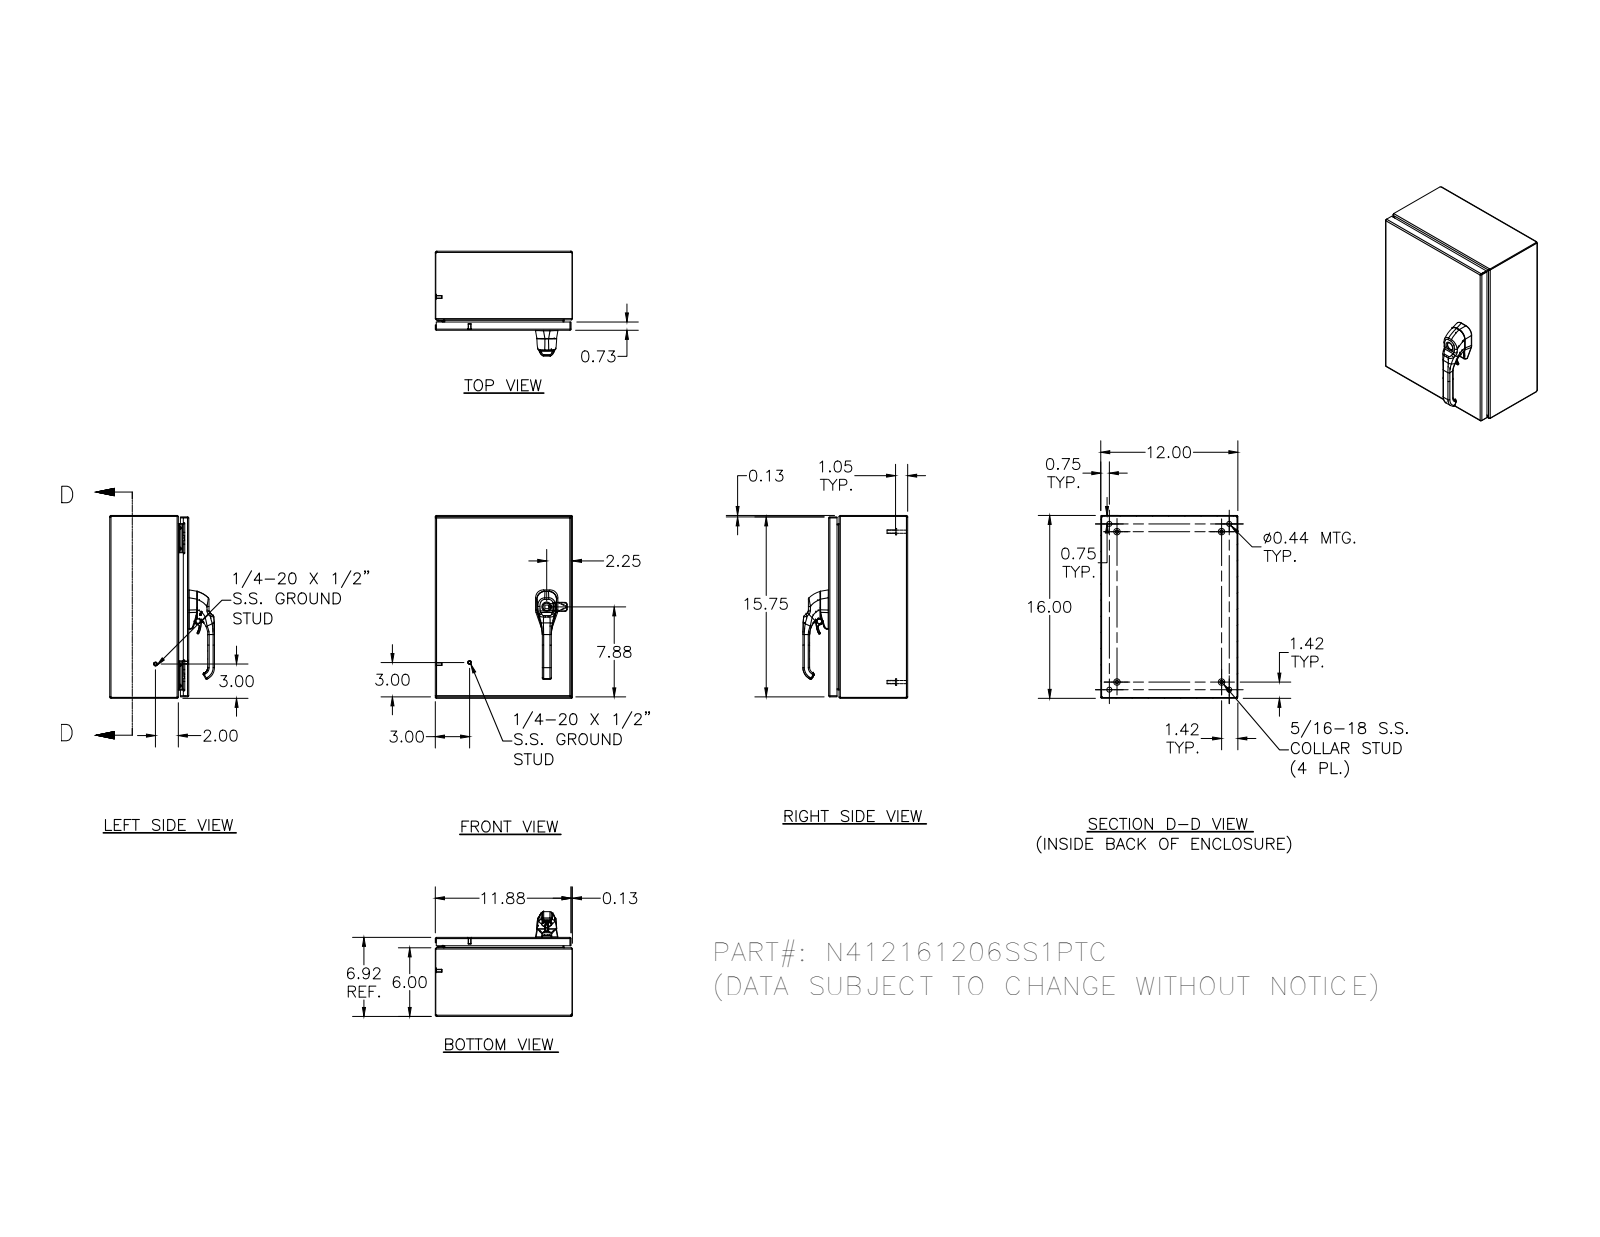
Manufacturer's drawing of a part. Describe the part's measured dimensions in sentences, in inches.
The part is named "N412161206SS1PTC; N412161206SS1PTCBKP; N4121612SS1PTCLID; HFW328176 (+8 more)". Its 3-D file was written by "Autodesk Inventor 2012 (AUTOMOTIVE_DESIGN)". It is 41 solids with 2782 faces: 882 planar, 1035 cylindrical and 865 other. Overall it measures 16 by 12 by 9.166 inches. Its volume is 69.21 cubic inches and its surface area 1 786 square inches. Round holes: 4 of diameter 0.093, 4 of diameter 0.152, 4 of diameter 0.167, 4 of diameter 0.172, 4 of diameter 0.188, 4 of diameter 0.437, 3 of diameter 0.213, 3 of diameter 0.281, 2 of diameter 0.156, 2 of diameter 0.315, 2 of diameter 0.402, 2 of diameter 0.413. Round bosses or shafts: 10 of diameter 0.25, 4 of diameter 0.563, 4 of diameter 0.36, 4 of diameter 0.32, 4 of diameter 0.3, 4 of diameter 0.275, 4 of diameter 0.256, 4 of diameter 0.164. Partial cylindrical surfaces (rounded edges, fillets, slot ends): 173 of radius 0.02, 101 of radius 0.012, 30 of radius 0.031, 26 of radius 0.05, 21 of radius 0.019, 20 of radius 0.105, 18 of radius 0.016, 14 of radius 0.079. The main face-to-face distances are 0.074, 6.843, 11.926, 6.917, 6.769, 15.926, 11.852, 12, 16, 15.852. The hole center spacings are 11.996, 0.017, 0.66, 12.656, 0.019, 0.5, 0.648, 0.656.
